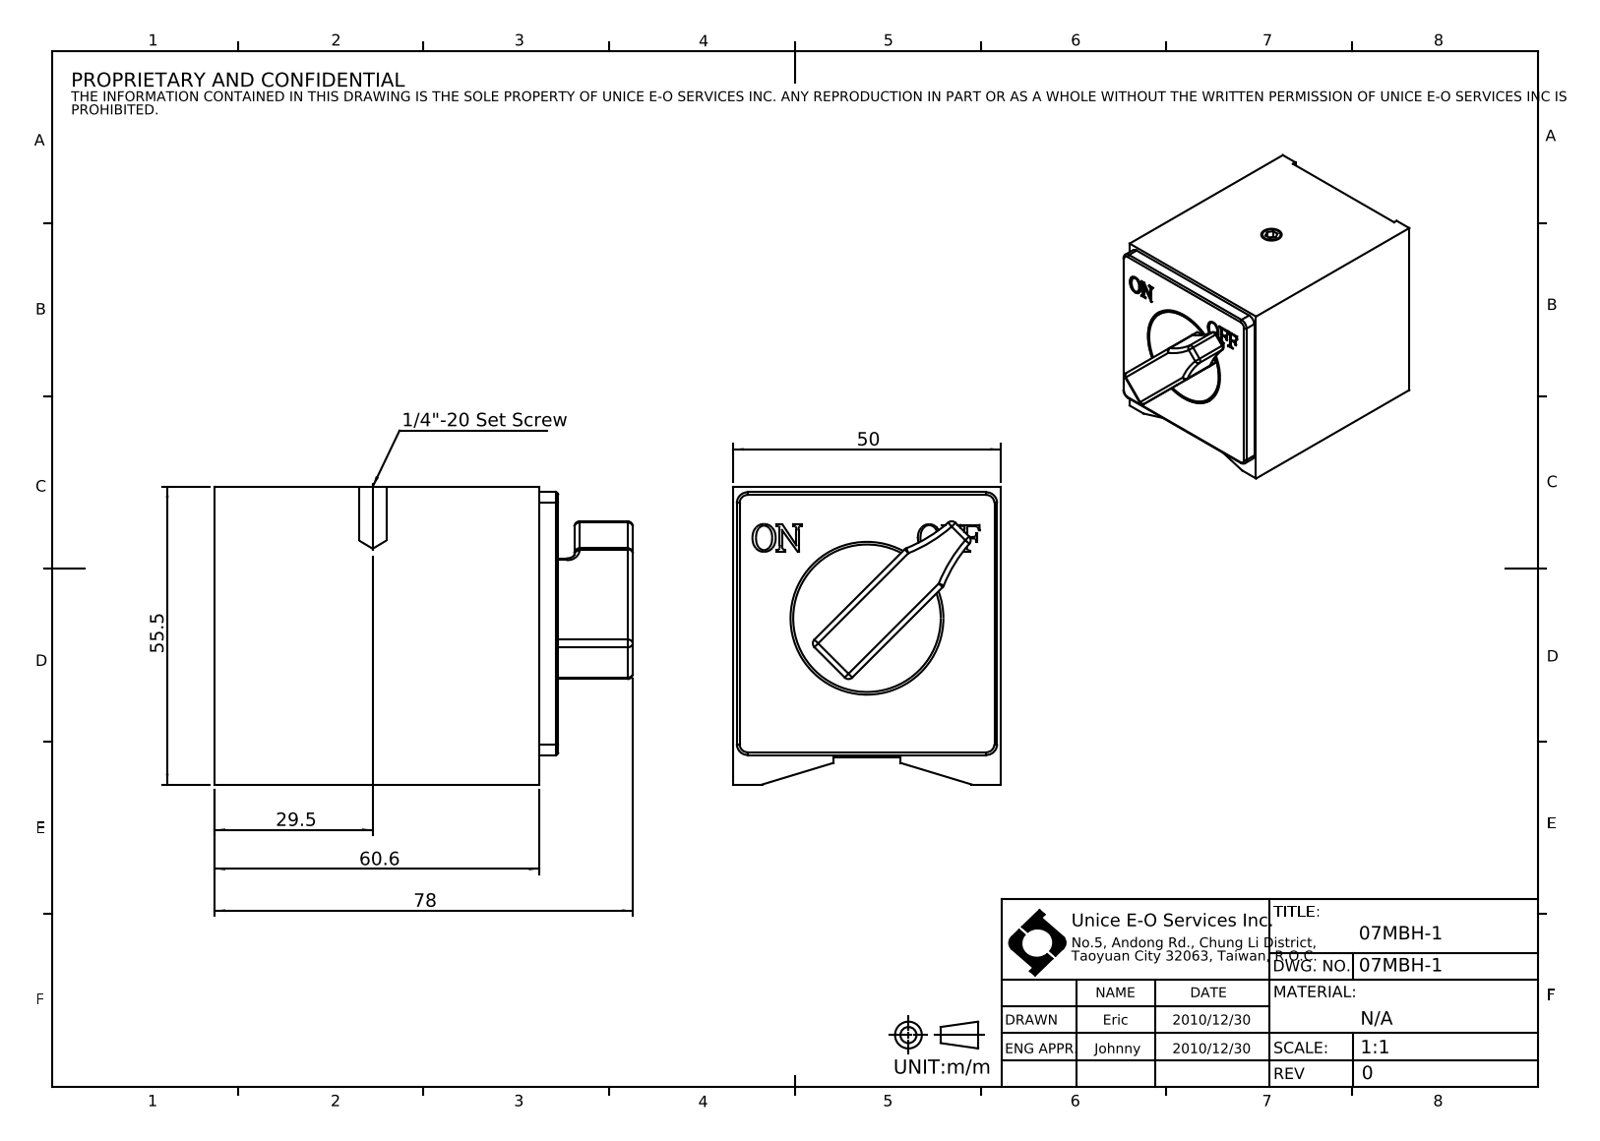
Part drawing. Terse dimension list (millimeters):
name: 07MBH-1
written by: SolidWorks 2016 (CONFIG_CONTROL_DESIGN)
unit: mm
bodies: 0 solids, 108 faces (49 planar, 31 cylindrical, 28 other)
size: 78 × 55.5 × 50
holes: 1× ⌀28.5
bosses: 1× ⌀27.5
rounds: 15× R1, 4× R0.5, 4× R2, 2× R27.35
face distances: 50, 63.1, 5, 50.5, 1, 55.5, 64.1, 10, 60.6, 59.6
